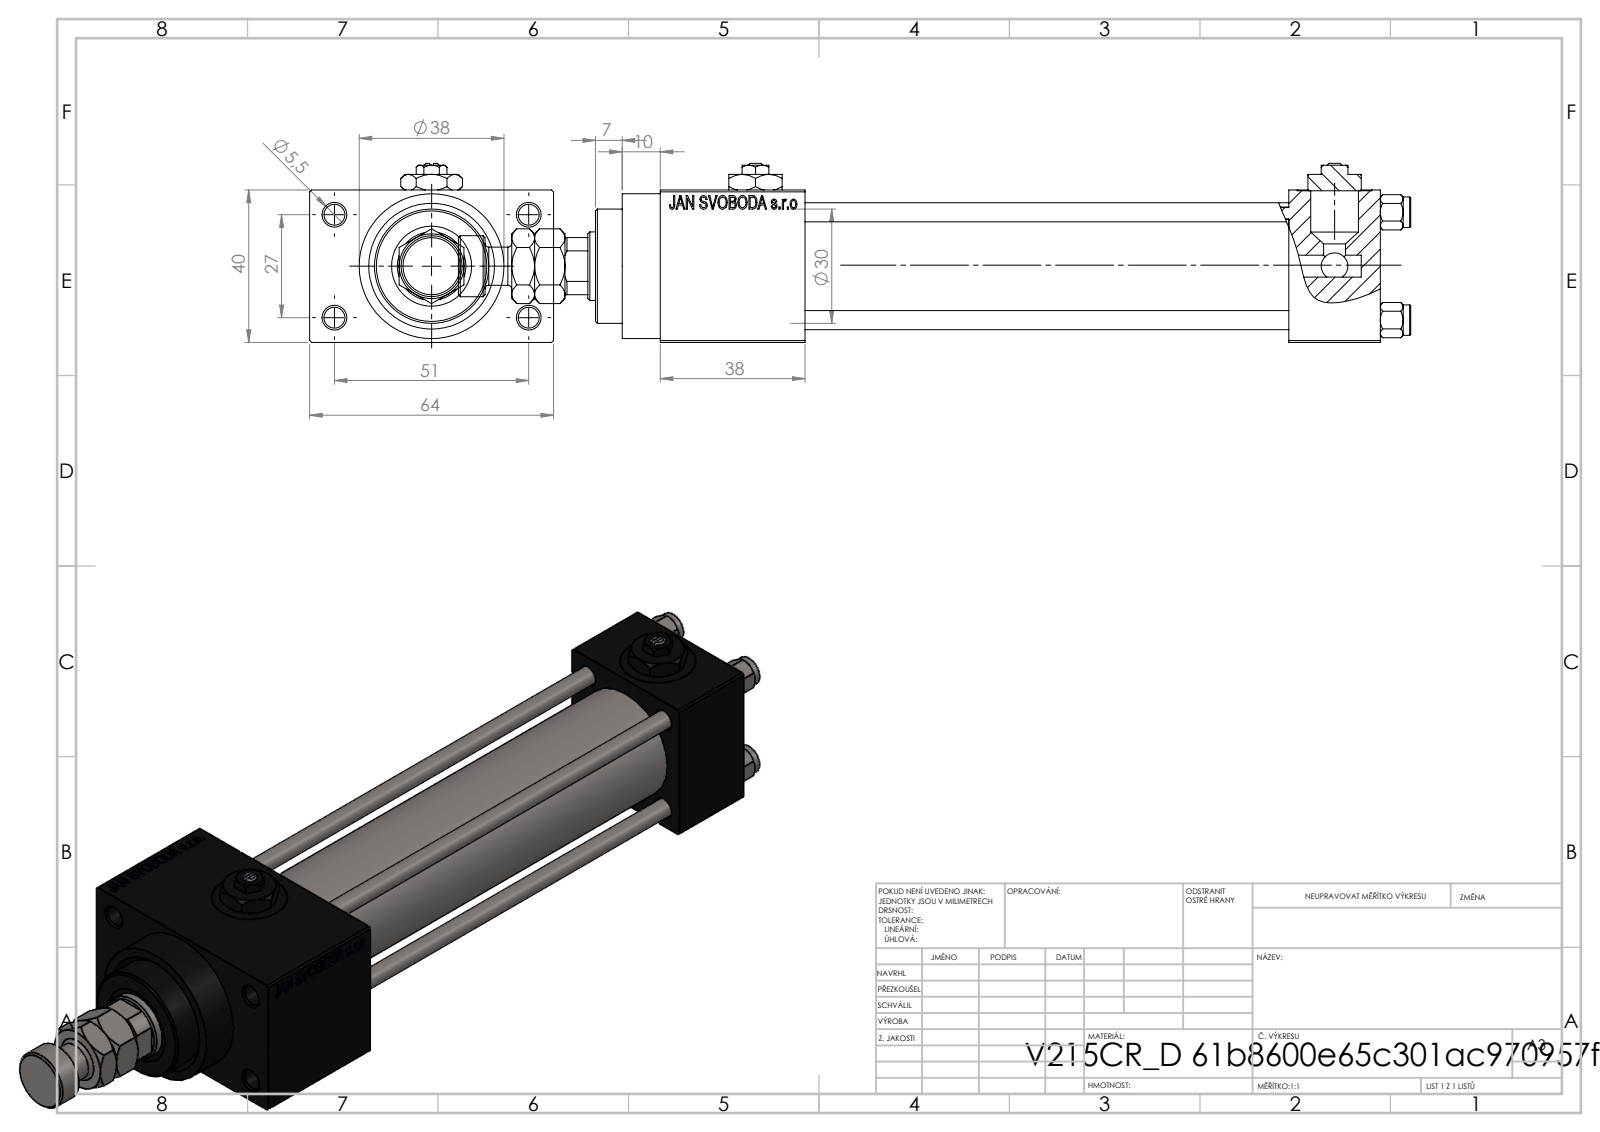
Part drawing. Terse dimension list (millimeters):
name: MFA; Zatka_pro_OIL_PORT; V215CR_D_Body; NUT_M5_D (+3 more)
written by: SolidWorks 2019 (CONFIG_CONTROL_DESIGN)
unit: mm
bodies: 14 solids, 1252 faces (557 planar, 101 cylindrical, 594 other)
size: 250 × 64 × 47
volume: 231 276 mm³; area: 91 965 mm²
holes: 5× ⌀20, 4× ⌀5, 4× ⌀5.5, 4× ⌀13.16, 3× ⌀7, 1× ⌀8.5, 1× ⌀18, 1× ⌀21, 1× ⌀25, 1× ⌀30
bosses: 4× ⌀8, 1× ⌀38, 1× ⌀31, 1× ⌀16, 1× ⌀10
rounds: 1× R8.5
face distances: 40, 12, 127, 24, 151, 52, 38, 165, 189, 64
hole spacings: 11.37, 20.01, 28.3, 28.85, 29.89, 39.66, 48.34, 27
